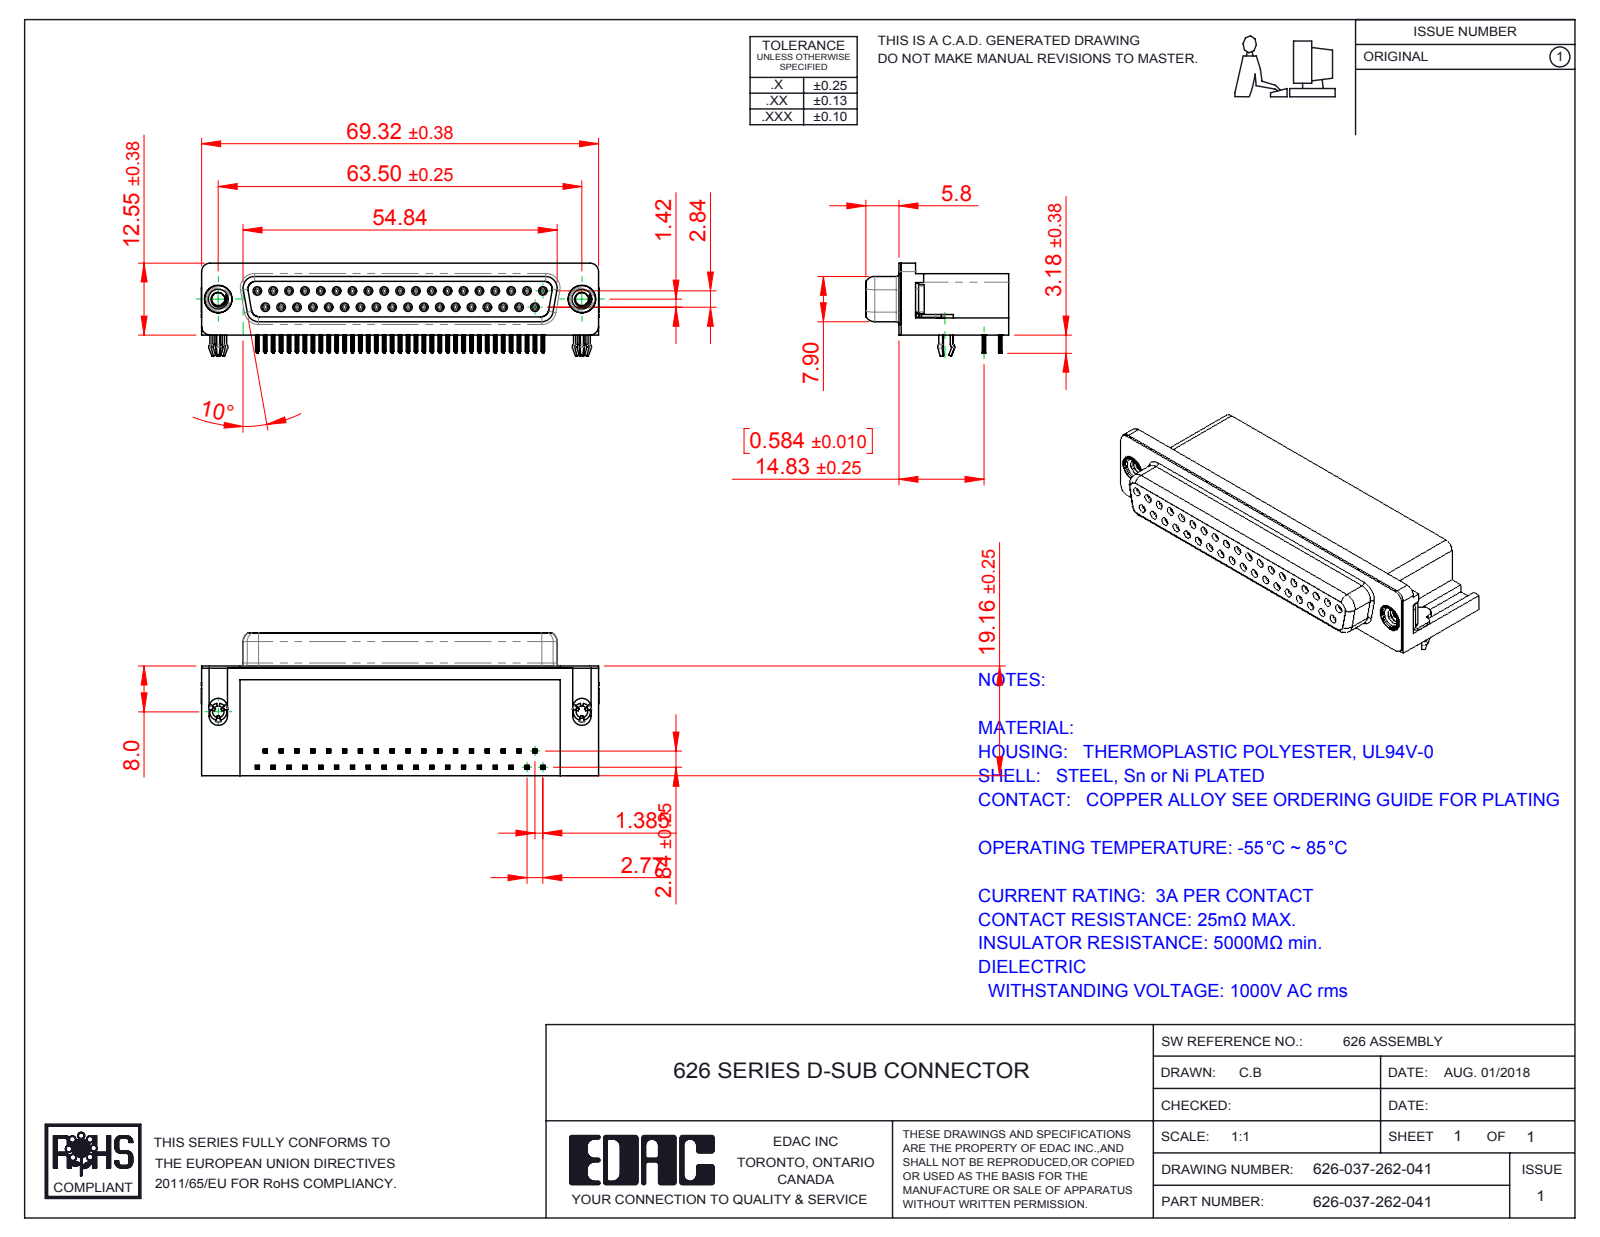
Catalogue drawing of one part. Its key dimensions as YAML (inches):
part_name: "626 3 Prong Board Lock; 626 Contact Top; 626 Housing_37 Socket; 626 Contact Bottom (+3 more)"
step_written_by: "SolidWorks 2016 (CONFIG_CONTROL_DESIGN)"
units: inches
bodies: {solids: 43, faces: 5664, planar: 2540, cylindrical: 1304, other: 1820}
overall_size: [2.732, 0.983, 0.64]
volume: 0.898
surface_area: 23.87
round_holes:
  - {diameter: 0.031, count: 37}
  - {diameter: 0.035, count: 37}
  - {diameter: 0.079, count: 2}
  - {diameter: 0.089, count: 2}
  - {diameter: 0.157, count: 2}
  - {diameter: 0.189, count: 2}
  - {diameter: 0.197, count: 2}
round_bosses_or_shafts:
  - {diameter: 0.047, count: 37}
  - {diameter: 0.193, count: 2}
  - {diameter: 0.187, count: 2}
  - {diameter: 0.154, count: 2}
  - {diameter: 0.118, count: 2}
partial_cylinders:
  - {radius: 0.004, count: 296}
  - {radius: 0.006, count: 148}
  - {radius: 0.014, count: 74}
  - {radius: 0.013, count: 37}
  - {radius: 0.011, count: 18}
  - {radius: 0.039, count: 18}
  - {radius: 0.01, count: 12}
  - {radius: 0.053, count: 8}
face_to_face_distances: [0.407, 0.016, 0.112, 0.244, 0.739, 0.018, 0.125, 0.033, 0.278, 0.262]
hole_center_spacings: [0.124, 0.109, 0.218, 0.327, 0.436, 0.872, 0.545, 0.763]
